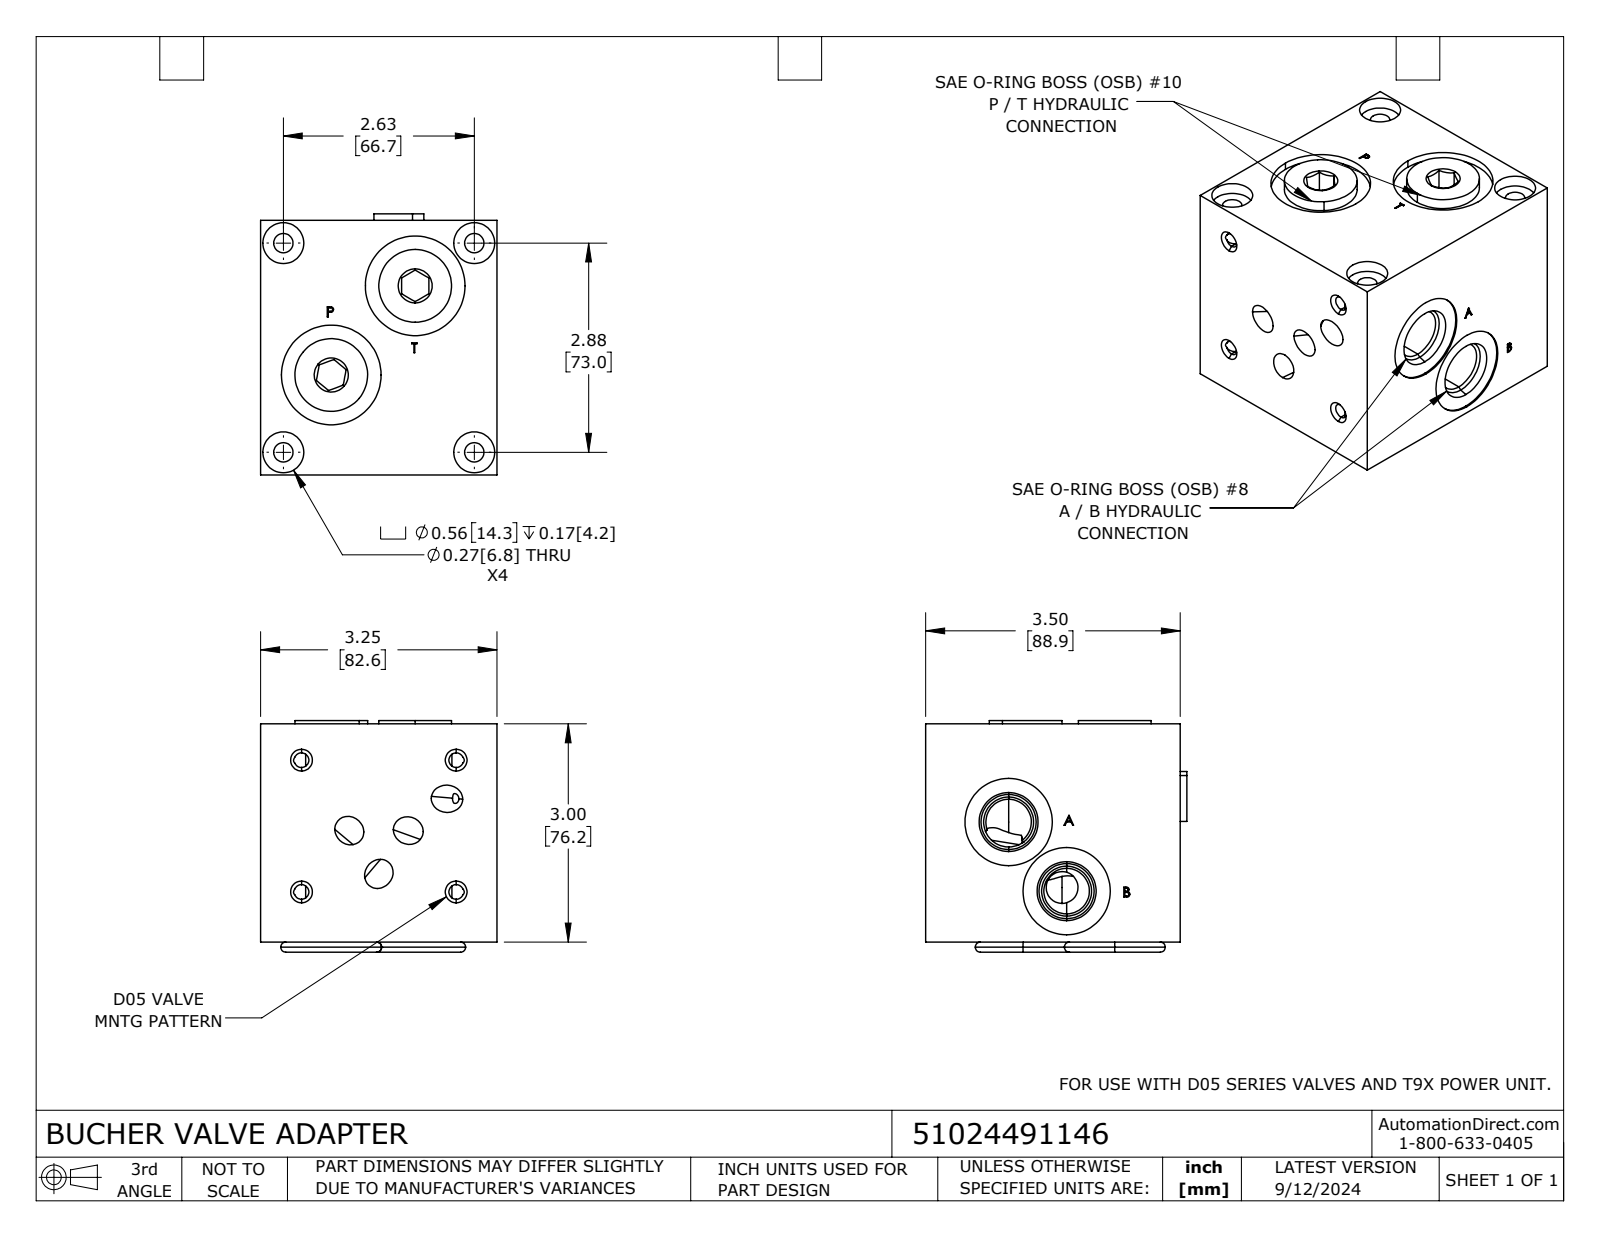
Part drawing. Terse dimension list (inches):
name: 51024491146
written by: SolidWorks 2023 (CONFIG_CONTROL_DESIGN)
unit: in
bodies: 9 solids, 582 faces (304 planar, 92 cylindrical, 186 other)
size: 3.59 × 3.25 × 3.184
volume: 30.49 in³; area: 112.4 in²
holes: 4× ⌀0.201, 4× ⌀0.266, 4× ⌀0.563, 2× ⌀0.375, 2× ⌀0.375, 2× ⌀0.437, 2× ⌀0.5, 2× ⌀0.686, 2× ⌀0.807, 2× ⌀1.2, 2× ⌀1.37, 1× ⌀0.511
bosses: 2× ⌀1, 2× ⌀0.868, 1× ⌀0.687, 1× ⌀0.559
rounds: 2× R0.306, 1× R0.313
face distances: 3.5, 3.25, 3, 0.105, 2.895, 0.02, 3.23, 0.045, 0.15, 3.045
hole spacings: 1.811, 2.126, 2.625, 2.793, 2.875, 3.893, 0.08, 0.934
